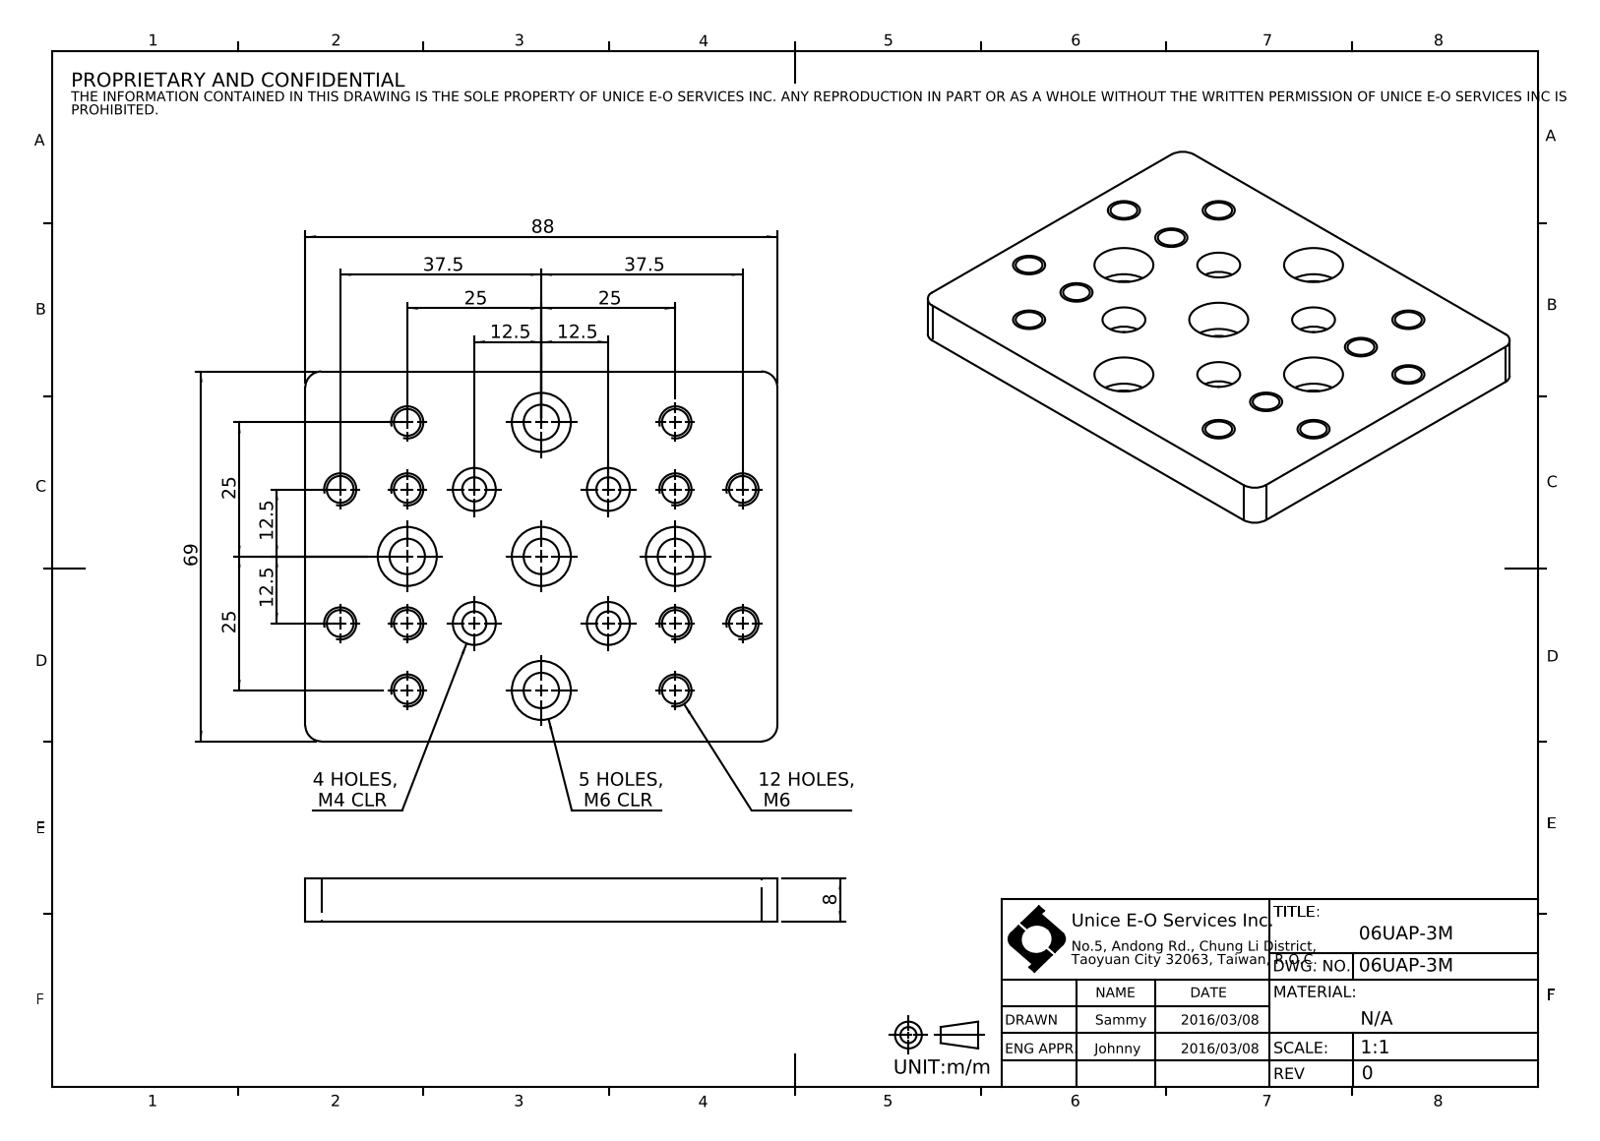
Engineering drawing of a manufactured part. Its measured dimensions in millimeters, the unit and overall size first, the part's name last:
Units: millimetres
Overall size (bounding box): 88 × 69 × 8
Round holes (diameter × count): ⌀5 ×12, ⌀6.6 ×5, ⌀11 ×5, ⌀4.5 ×4, ⌀8 ×4
Partial cylindrical surfaces — rounded edges, fillets, slot ends (radius × count): R3 ×4
Main face-to-face distances: 8, 69, 88, 2, 6, 3.6, 1.6, 4.4
Hole centre spacings: 39.53, 17.68, 25, 12.5, 27.95, 35.36, 55.9, 50
Volume: 42 322 mm³ · Surface area: 17 057 mm²
Bodies: 1 solid, 79 faces (15 planar, 64 cylindrical, 0 other)
Part name (STEP PRODUCT): 06UAP-3M
STEP written by: SolidWorks 2016 (CONFIG_CONTROL_DESIGN)
